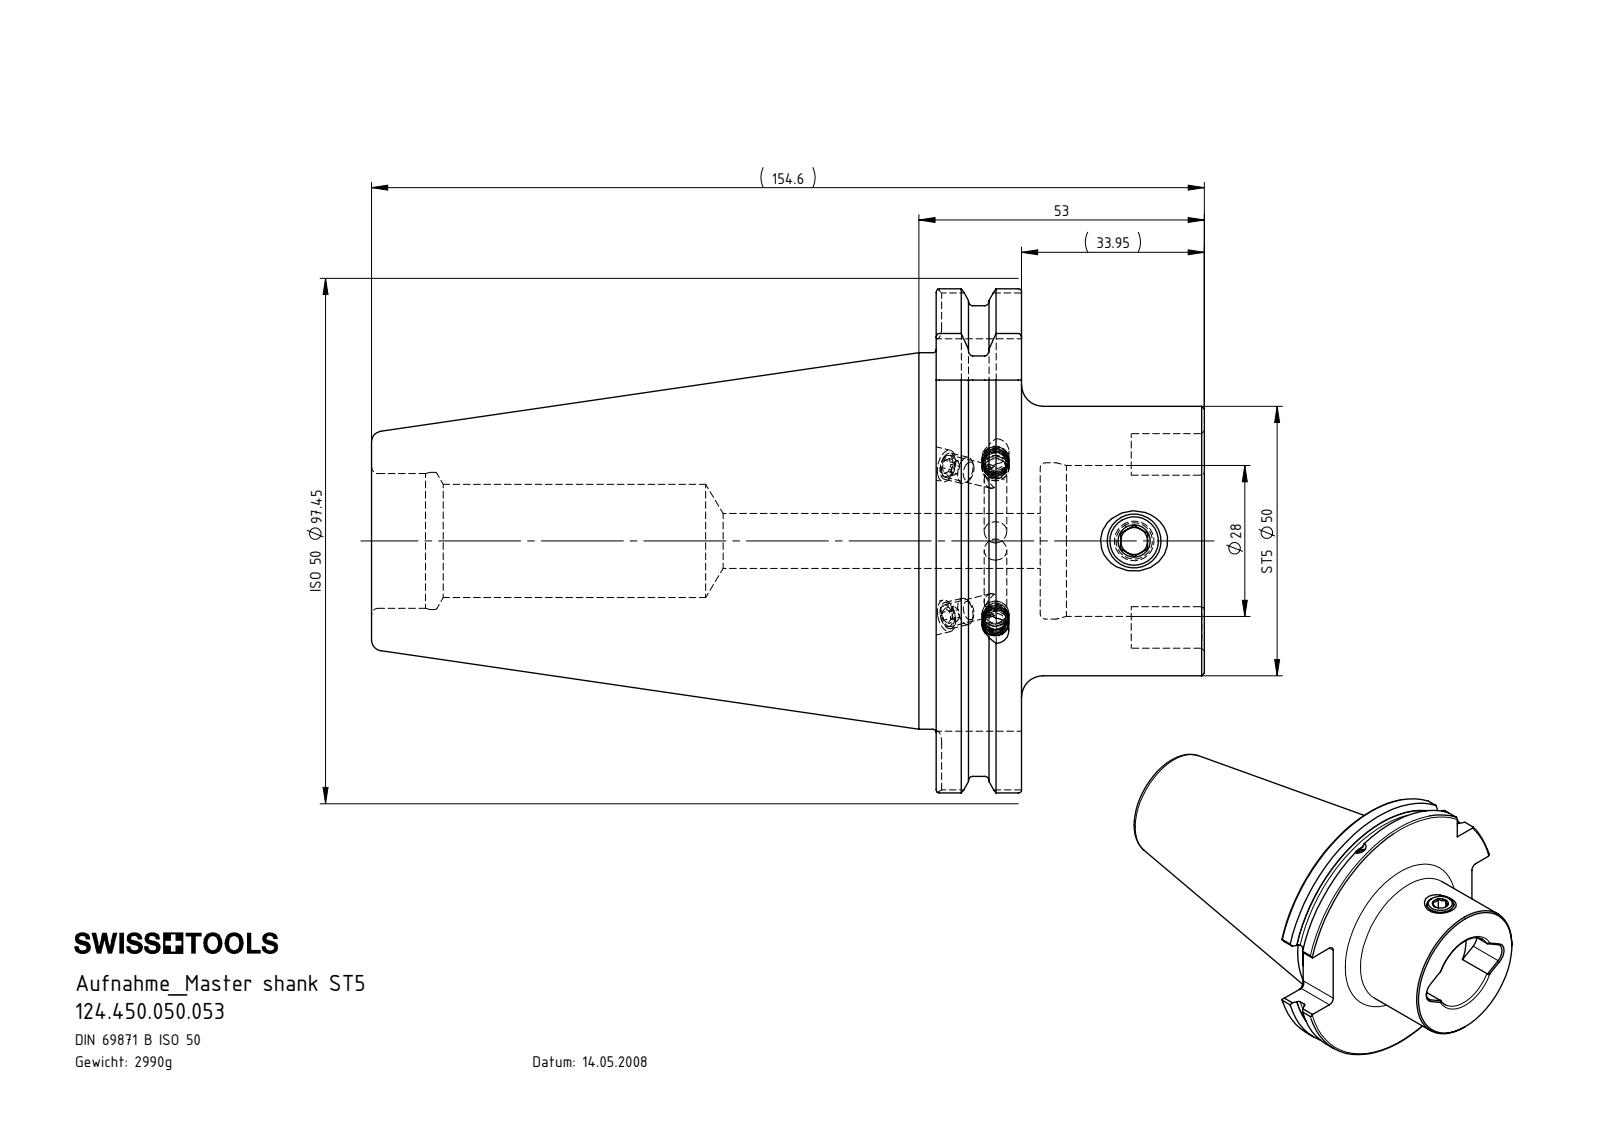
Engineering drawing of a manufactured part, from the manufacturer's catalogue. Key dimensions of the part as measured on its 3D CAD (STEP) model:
Part name (STEP PRODUCT): ST5-ER1.001.012_A; SB5-ST5.K01.053_A_mit Bundkhlung; ISO 4026 - M5 x 5_PreviewCfg; SB5-ST5.K01.053 (+2 more)
STEP written by: SolidWorks 2015 (CONFIG_CONTROL_DESIGN)
Units: millimetres
Bodies: 9 solids, 292 faces (81 planar, 74 cylindrical, 137 other)
Overall size (bounding box): 154.6 × 97.45 × 93.51
Volume: 381 071 mm³ · Surface area: 52 314 mm²
Round holes (diameter × count): ⌀4.2 ×3, ⌀4 ×2, ⌀6 ×2, ⌀5 ×1, ⌀9 ×1, ⌀10.2 ×1, ⌀21 ×1, ⌀25 ×1, ⌀25.45 ×1, ⌀28 ×1, ⌀29 ×1
Round bosses / shafts (diameter × count): ⌀5 ×3, ⌀91 ×1, ⌀69.85 ×1, ⌀50 ×1, ⌀10 ×1, ⌀6 ×1
Partial cylindrical surfaces — rounded edges, fillets, slot ends (radius × count): R2 ×8, R4.2 ×2, R48.73 ×1
Main face-to-face distances: 15.85, 49.8, 33.95, 19.3, 3.45, 30.5, 104.8, 120.65, 124.1, 154.6
